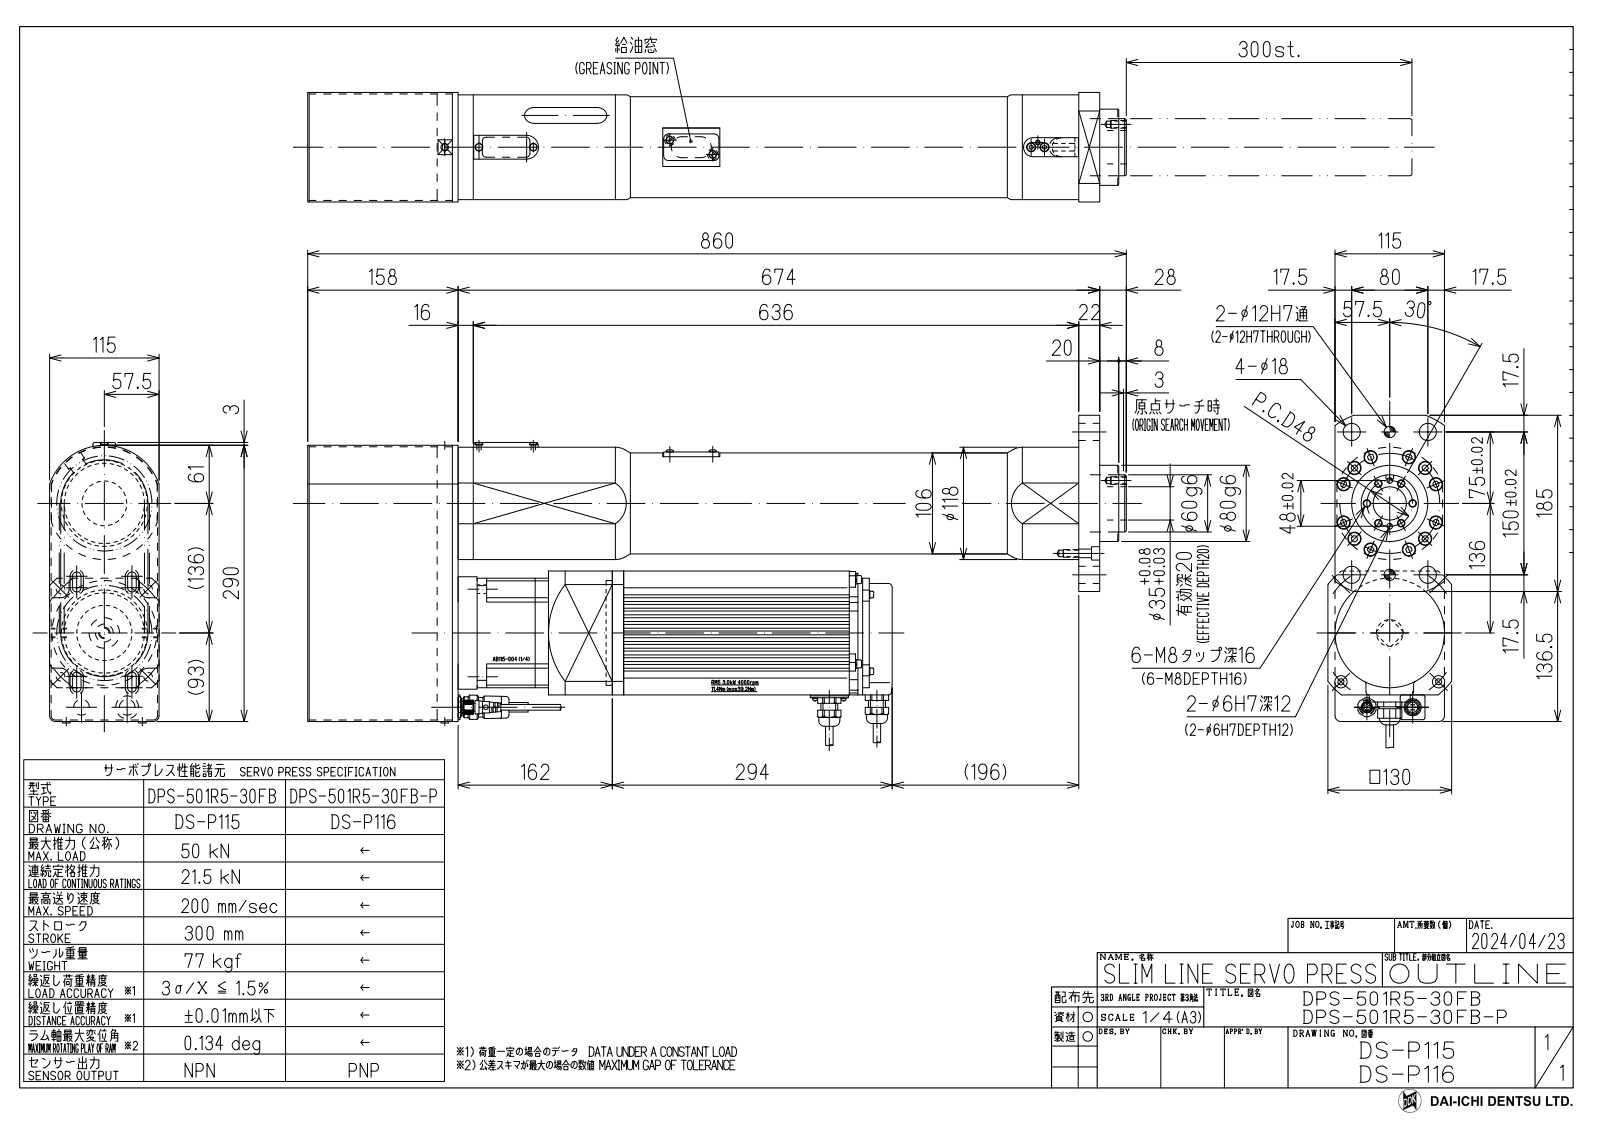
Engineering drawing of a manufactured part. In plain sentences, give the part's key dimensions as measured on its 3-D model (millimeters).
The part is named "DPS-501R5-30FB(-P)(DS-P115_P116)_OUTLINE; DPS-501R5-30FB(DS-P115)_BODY; DPS-501(300st)_SHAFT". Its 3-D file was written by "Autodesk Inventor 2023 (CONFIG_CONTROL_DESIGN)". It is 2 solids with 1650 faces: 1009 planar, 365 cylindrical and 276 other. Overall it measures 860 by 345.51 by 130 millimeters. Its volume is 17 940 000 cubic millimeters and its surface area 1 019 000 square millimeters. Round holes: 12 of diameter 14, 6 of diameter 6.65, 4 of diameter 3.2, 4 of diameter 8.2, 4 of diameter 9, 4 of diameter 18, 3 of diameter 1.2, 3 of diameter 6, 2 of diameter 6.75, 2 of diameter 8, 2 of diameter 9.5, 2 of diameter 11. Round bosses or shafts: 20 of diameter 13, 11 of diameter 8, 7 of diameter 1, 6 of diameter 8.5, 4 of diameter 15.4, 4 of diameter 6, 4 of diameter 4, 3 of diameter 18. Partial cylindrical surfaces (rounded edges, fillets, slot ends): 40 of radius 5, 17 of radius 2, 12 of radius 4.25, 9 of radius 1, 8 of radius 3, 7 of radius 4, 4 of radius 8.5, 4 of radius 10. The main face-to-face distances are 3, 6, 9, 115, 65, 68, 62, 71, 24, 28. The hole center spacings are 52.5, 74.24, 20.48, 40.18, 58.33, 87.3, 97, 102.97.
